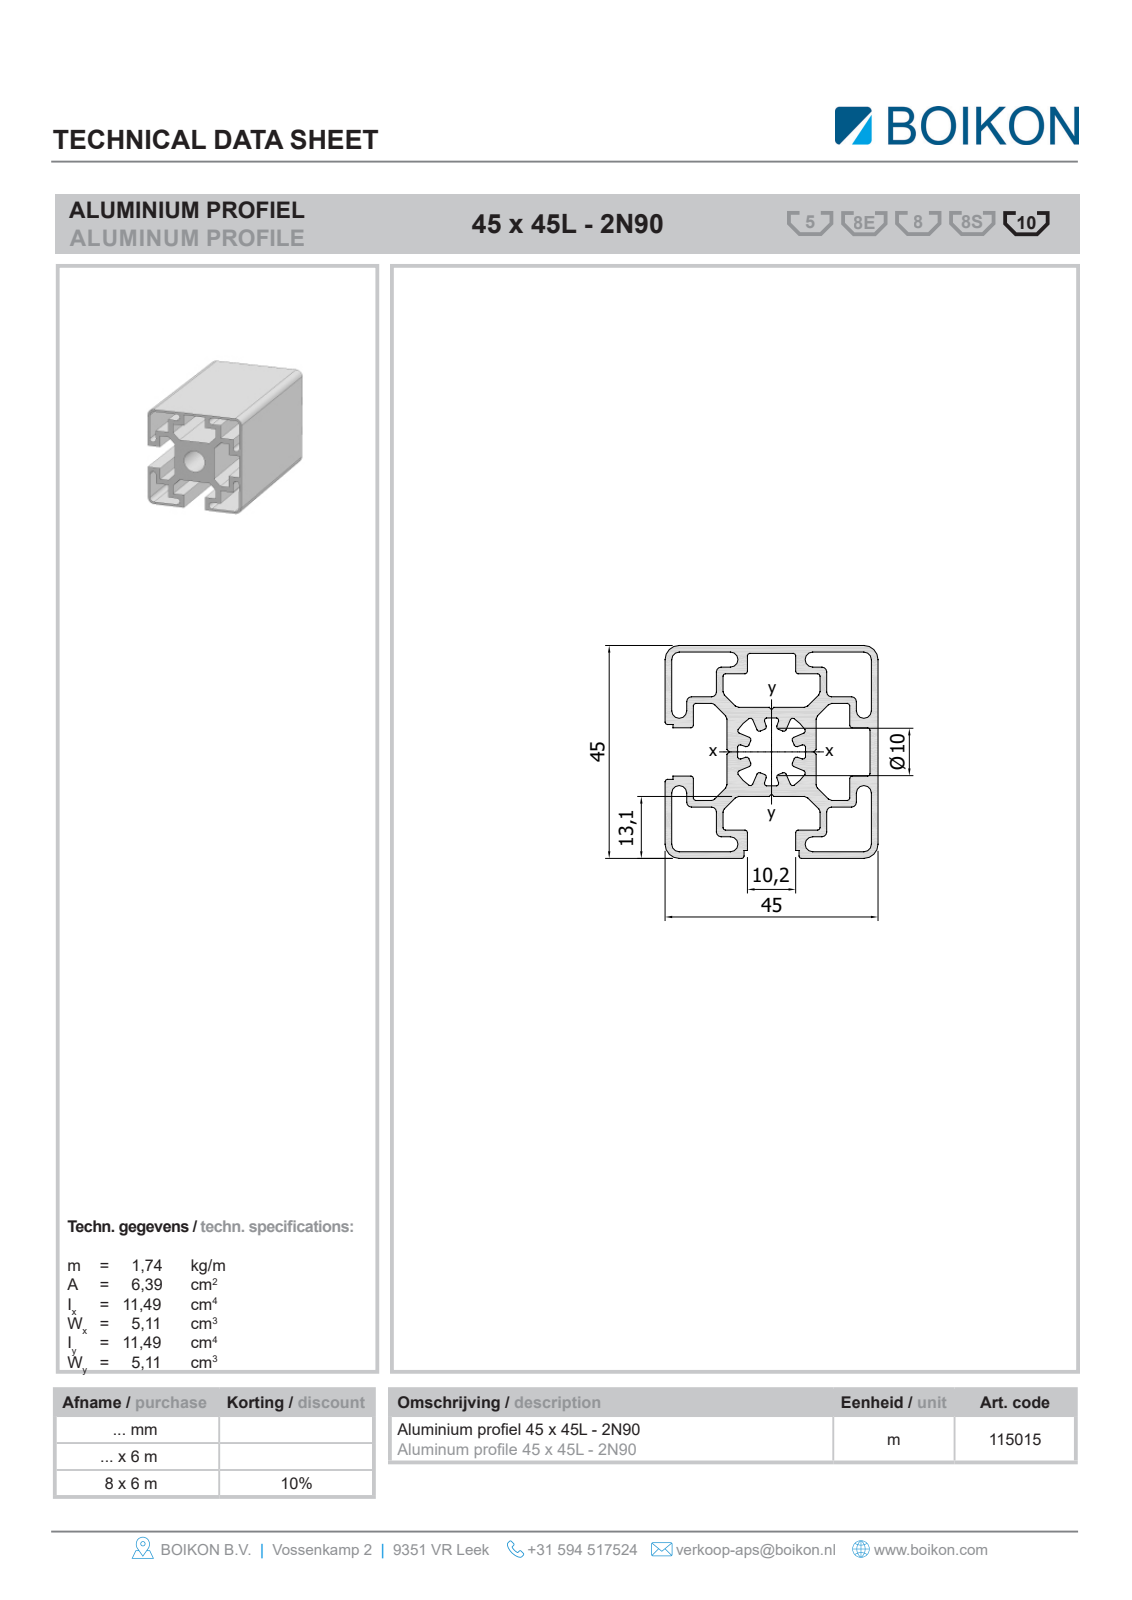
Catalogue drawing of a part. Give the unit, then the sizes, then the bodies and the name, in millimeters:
Units: millimetres
Overall size (bounding box): 1000 × 45 × 45
Round holes (diameter × count): ⌀10 ×1
Partial cylindrical surfaces — rounded edges, fillets, slot ends (radius × count): R2 ×4, R3 ×4
Main face-to-face distances: 1, 44, 10, 35, 9, 34, 45, 13.1, 3.1, 31.9
Volume: 850 008 mm³ · Surface area: 558 004 mm²
Bodies: 1 solid, 71 faces (62 planar, 9 cylindrical, 0 other)
Part name (STEP PRODUCT): Root; 11501545x45L-2N90BOIKON0
STEP written by: HiCAD 2013 1802.4 Build 509 (AUTOMOTIVE_DESIGN)
